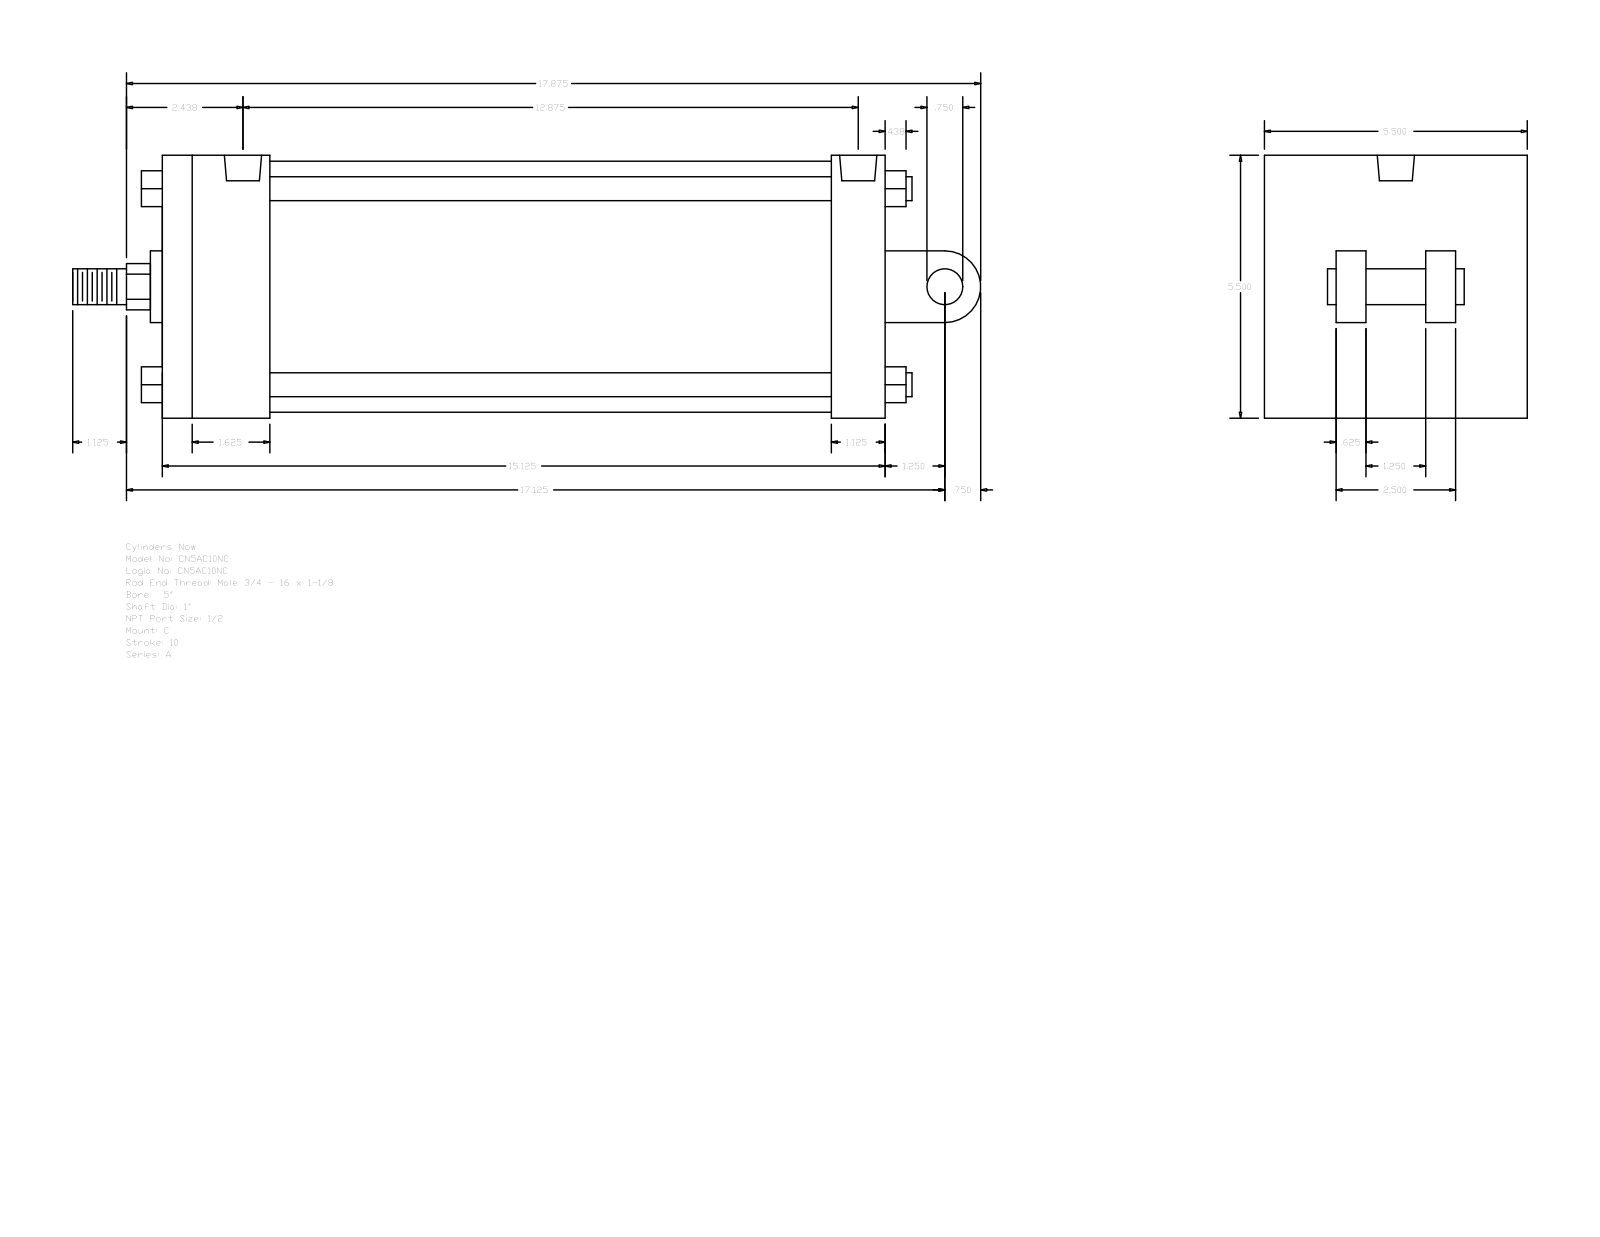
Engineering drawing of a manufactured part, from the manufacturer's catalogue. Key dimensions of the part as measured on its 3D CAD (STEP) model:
Part name (STEP PRODUCT): A_C__0500_1
STEP written by: GSSL Pune (CONFIG_CONTROL_DESIGN)
Units: millimetres
Bodies: 0 solids, 135 faces (102 planar, 33 cylindrical, 0 other)
Overall size (bounding box): 482.6 × 139.7 × 139.7
Round holes (diameter × count): ⌀8.73 ×4, ⌀19.77 ×2
Round bosses / shafts (diameter × count): ⌀12.7 ×4, ⌀19.05 ×2, ⌀133.35 ×1, ⌀38.1 ×1, ⌀25.4 ×1
Partial cylindrical surfaces — rounded edges, fillets, slot ends (radius × count): R12.29 ×1, R19.05 ×1
Main face-to-face distances: 139.7, 384.18, 57.15, 355.6, 298.45, 327.03, 28.58, 38.1, 101.6, 53.97
Hole centre spacings: 2.39, 322.25, 324.64, 327.03
